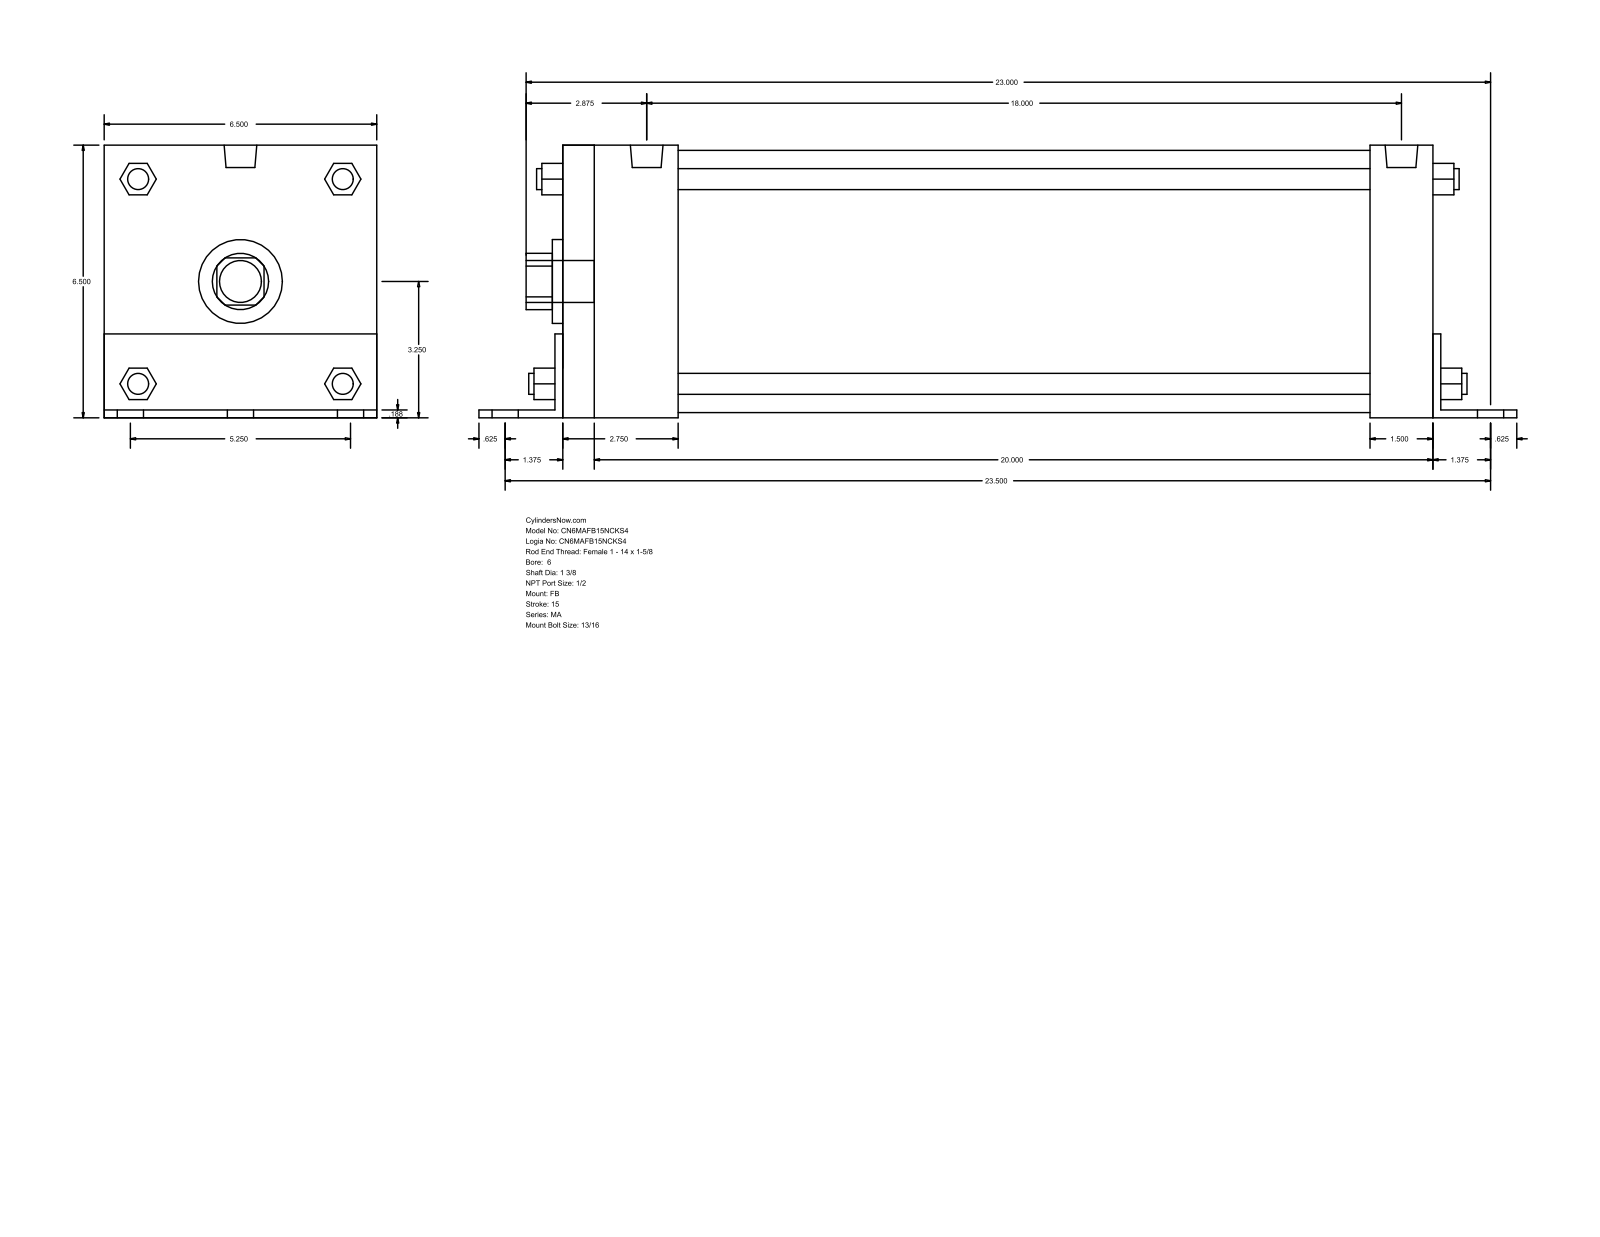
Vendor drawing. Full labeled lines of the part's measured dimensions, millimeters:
Part name (STEP PRODUCT): MA_FB__0600_1.375
STEP written by: GSSL Pune (CONFIG_CONTROL_DESIGN)
Units: millimetres
Bodies: 0 solids, 140 faces (105 planar, 35 cylindrical, 0 other)
Overall size (bounding box): 625.48 × 165.15 × 165.1
Round holes (diameter × count): ⌀34.92 ×1, ⌀50.8 ×1, ⌀158.75 ×1
Round bosses / shafts (diameter × count): ⌀20.64 ×6, ⌀17.46 ×4, ⌀12.7 ×4, ⌀19.77 ×2, ⌀25.4 ×1
Partial cylindrical surfaces — rounded edges, fillets, slot ends (radius × count): R17.06 ×1, R32.05 ×1
Main face-to-face distances: 165.1, 4.76, 523.87, 165.15, 4.71, 160.39, 4.77, 38.1, 528.64, 533.4
